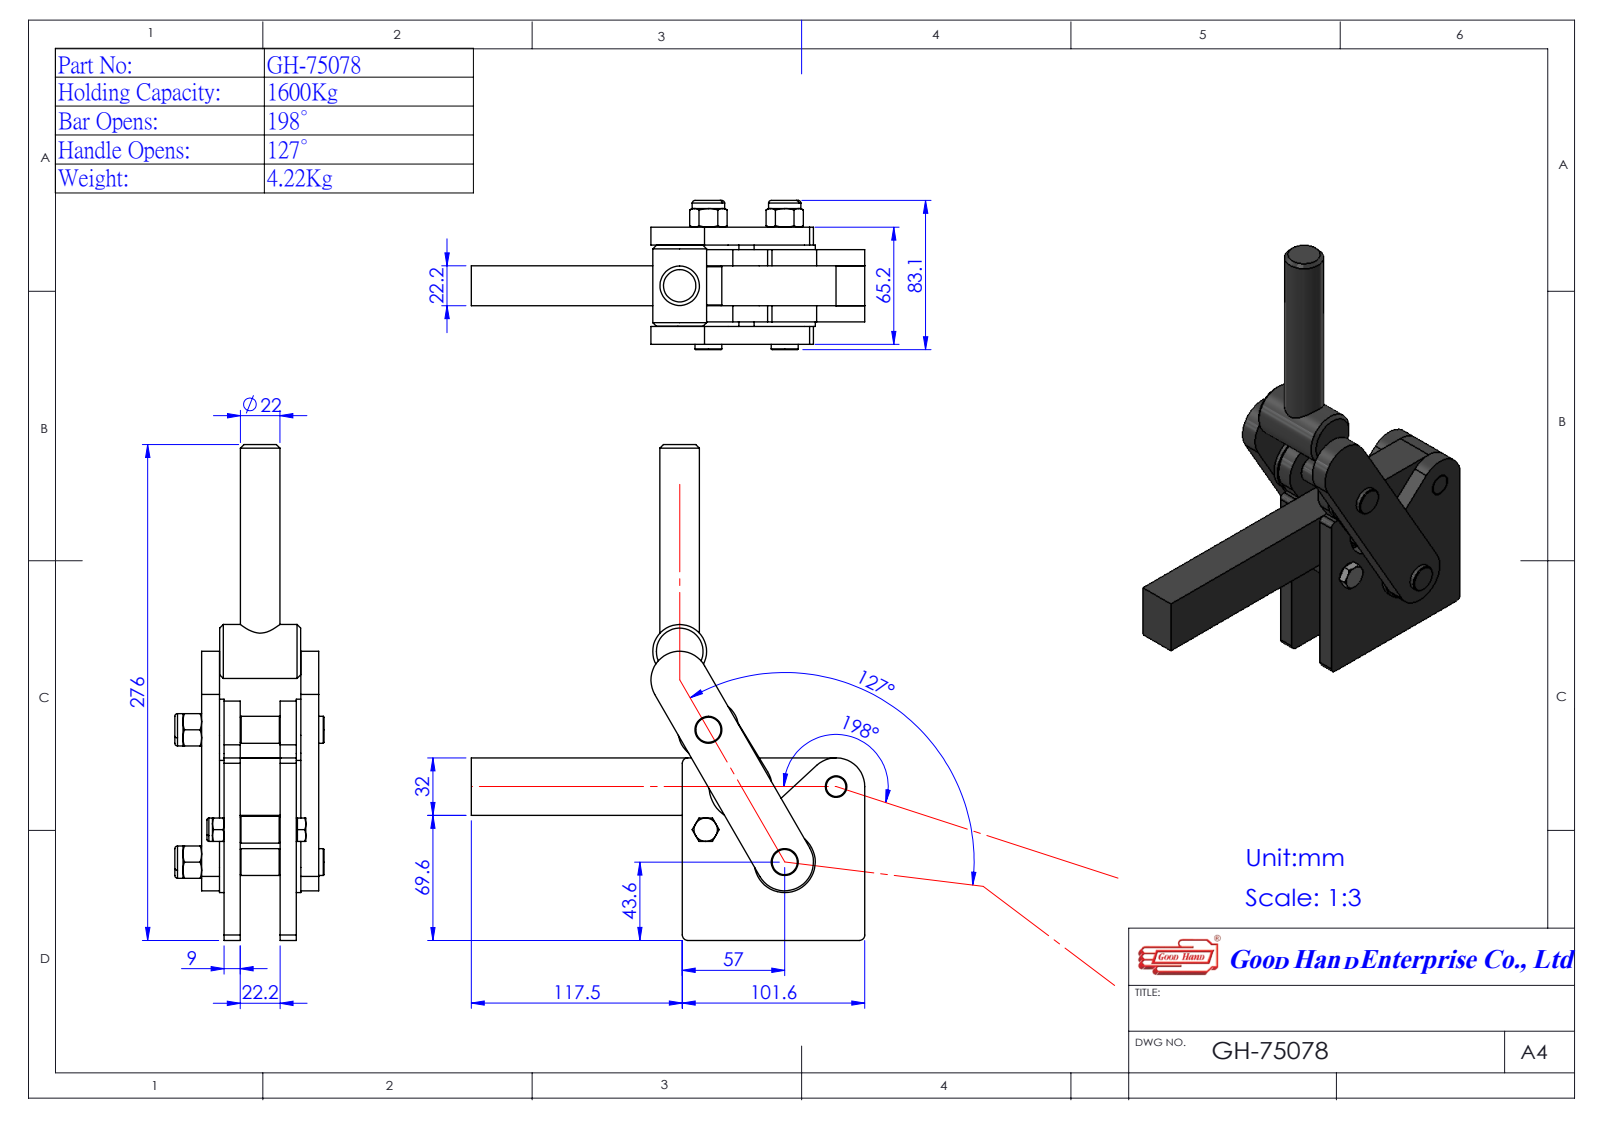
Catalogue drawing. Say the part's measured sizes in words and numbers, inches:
The part is named "GH-75078(簡化); 4704808-1^GH-75078(簡化); Group4^GH-75078(簡化); Group5^GH-75078(簡化) (+1 more)". Its 3-D file was written by "SolidWorks 2016 (AUTOMOTIVE_DESIGN)". It is 5 solids with 214 faces: 89 planar, 65 cylindrical and 60 other. Overall it measures 10.866 by 8.626 by 3.093 inches. Its volume is 32.83 cubic inches and its surface area 195.6 square inches. Round holes: 3 of diameter 0.354. Round bosses or shafts: 3 of diameter 0.591, 2 of diameter 1.339, 1 of diameter 1.181, 1 of diameter 0.866, 1 of diameter 0.512, 1 of diameter 0.354. Partial cylindrical surfaces (rounded edges, fillets, slot ends): 5 of radius 0.63, 3 of radius 0.118, 1 of radius 0.748. The main face-to-face distances are 0.354, 1.228, 0.874, 1.583, 0.492, 0.846, 1.72, 2.075, 1.26, 0.098. The hole center spacings are 1.46, 2.037, 3.063.
